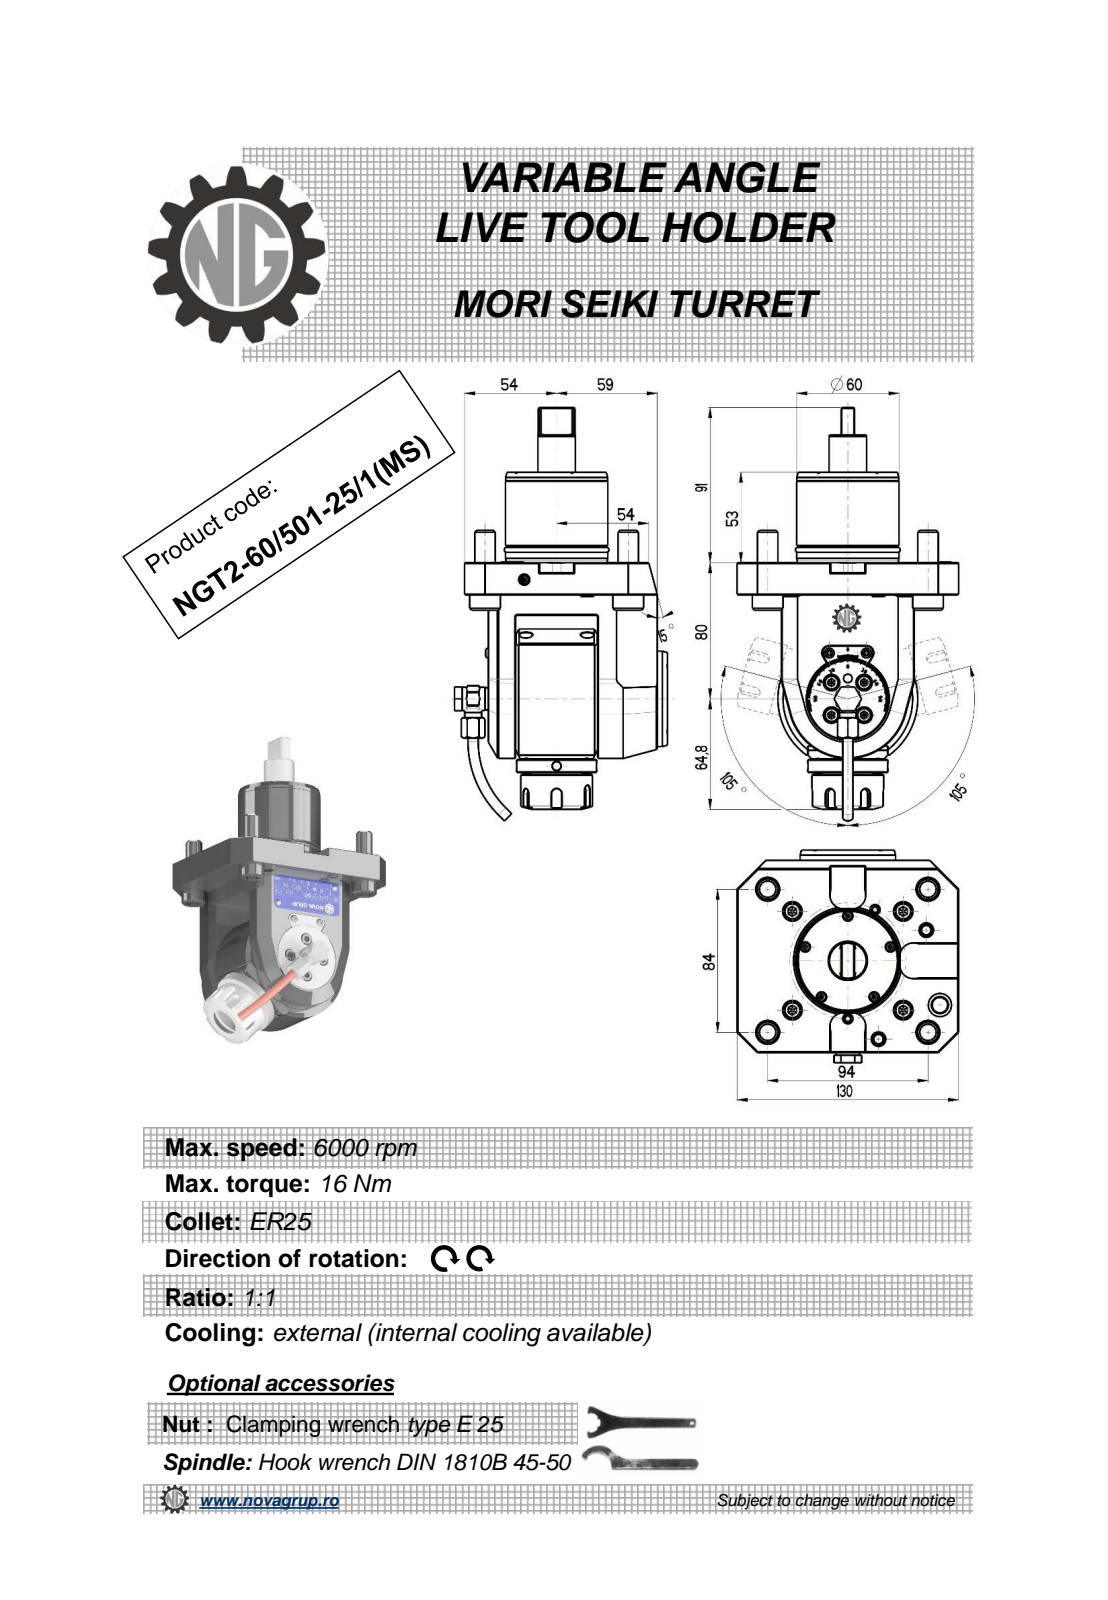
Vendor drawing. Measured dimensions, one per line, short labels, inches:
name: NGT2_60_501_25_1_MS
written by: PRO/ENGINEER BY PARAMETRIC TECHNOLOGY CORPORATION, 2010280 (CONFIG_CONTROL_DESIGN)
unit: in
bodies: 2 solids, 642 faces (259 planar, 197 cylindrical, 186 other)
size: 9.554 × 5.118 × 4.917
volume: 67.07 in³; area: 166.9 in²
holes: 3× ⌀0.157, 2× ⌀0.197, 2× ⌀0.354, 1× ⌀0.118, 1× ⌀0.244, 1× ⌀0.394, 1× ⌀0.433, 1× ⌀0.799
bosses: 4× ⌀0.709, 4× ⌀0.472, 2× ⌀0.315, 2× ⌀0.236, 2× ⌀0.224, 1× ⌀3.228, 1× ⌀2.362, 1× ⌀2.354
rounds: 20× R0.014, 12× R0.016, 10× R0.004, 10× R0.118, 6× R0.315, 5× R0.108, 4× R0.02, 2× R0.031
face distances: 0.748, 0.236, 0.472, 1.22, 3.071, 1.024, 4.094, 3.898, 0.63, 2.835
hole spacings: 0.016, 1.553, 1.929, 1.945, 2.311, 2.317, 2.359
